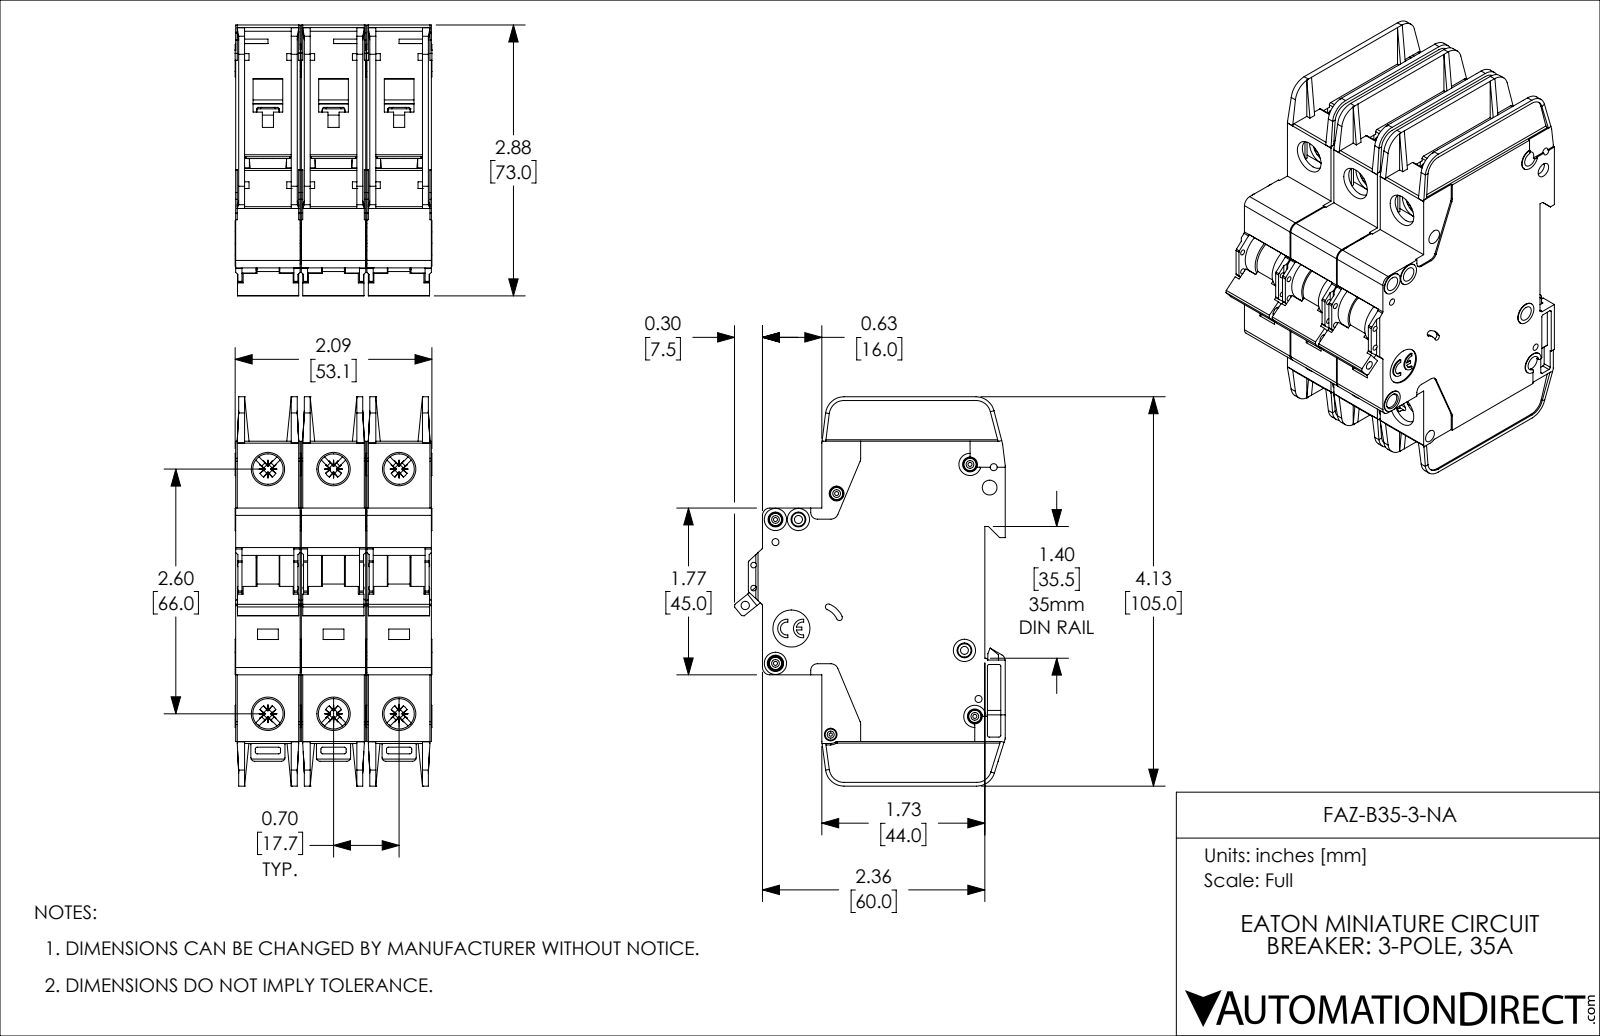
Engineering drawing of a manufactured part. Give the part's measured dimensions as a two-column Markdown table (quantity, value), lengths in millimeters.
| quantity | value |
| --- | --- |
| part name | FAZ-B35-3-NA |
| STEP written by | SolidWorks 2019 (AUTOMOTIVE_DESIGN) |
| units | millimeters |
| bodies | 3 solids, 3381 faces (2013 planar, 1071 cylindrical, 297 other) |
| overall size | 105 × 73.1 × 53.1 |
| volume | 230 200 mm³ |
| surface area | 79 350 mm² |
| round holes (diameter × count) | 4 × 8, 8.2 × 6, 1.1 × 5, 1.9 × 4, 1.5 × 2, 2.2 × 2, 0.9 × 1, 2.3 × 1, 2.5 × 1, 3.4 × 1, 10 × 1 |
| round bosses / shafts (diameter × count) | 3.3 × 5, 6 × 4, 3 × 4, 2.5 × 3 |
| partial cylindrical surfaces (radius × count) | 0.5 × 72, 0.4 × 30, 1 × 18, 1.1 × 12, 2 × 12, 0.2 × 6, 0.3 × 6, 0.7 × 6 |
| main face-to-face distances | 17.7, 1.2, 35.4, 17.4, 15, 35.1, 18.9, 16.5, 2.7, 2.4 |
| hole center spacings | 17.7, 68.3, 66, 6.2, 13.6, 22.1, 35.4, 74.9 |
